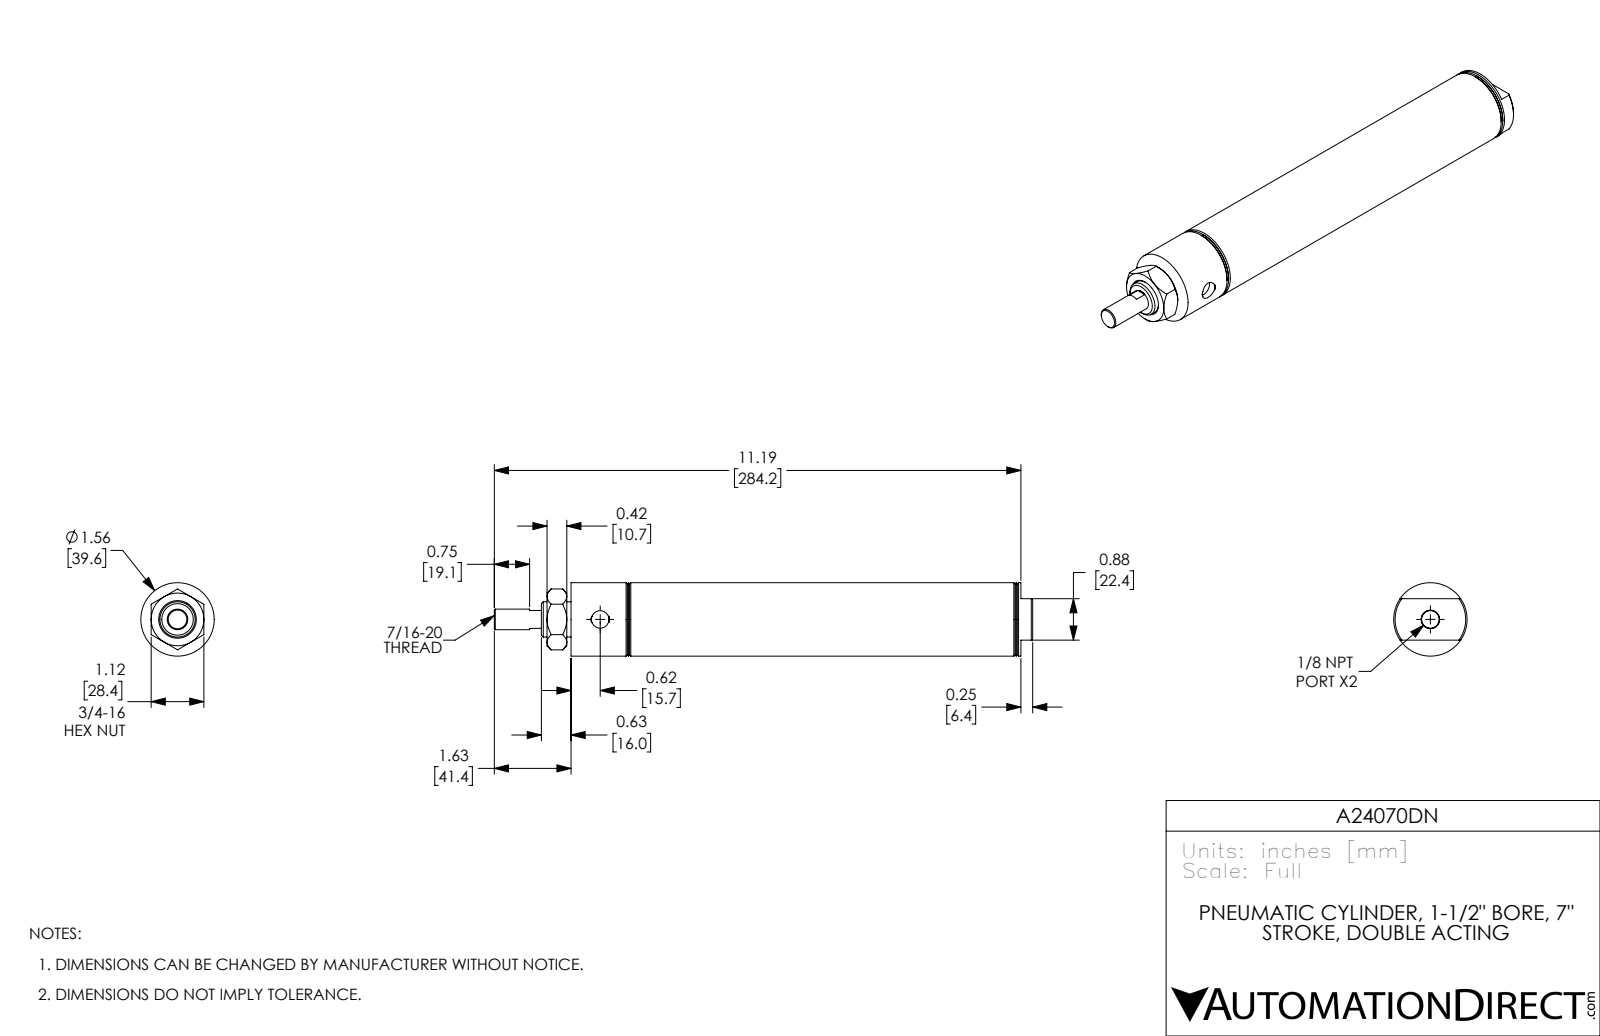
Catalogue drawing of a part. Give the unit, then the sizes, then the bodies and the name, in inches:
Units: inches
Overall size (bounding box): 11.44 × 1.56 × 1.56
Round holes (diameter × count): ⌀0.374 ×2, ⌀0.437 ×1, ⌀0.75 ×1, ⌀1.5 ×1
Round bosses / shafts (diameter × count): ⌀1.56 ×1, ⌀0.746 ×1
Main face-to-face distances: 0.5, 7.5, 7, 8.84, 8.34, 1.34, 0.97, 1.47, 8.47, 9.81
Volume: 7.907 in³ · Surface area: 118.5 in²
Bodies: 3 solids, 104 faces (32 planar, 24 cylindrical, 48 other)
Part name (STEP PRODUCT): A24070DN; A24070DN_Mounting Nut_D-3556; A24070DN-Rod; A24070DN-MainBody
STEP written by: SolidWorks 2017 (AUTOMOTIVE_DESIGN)
